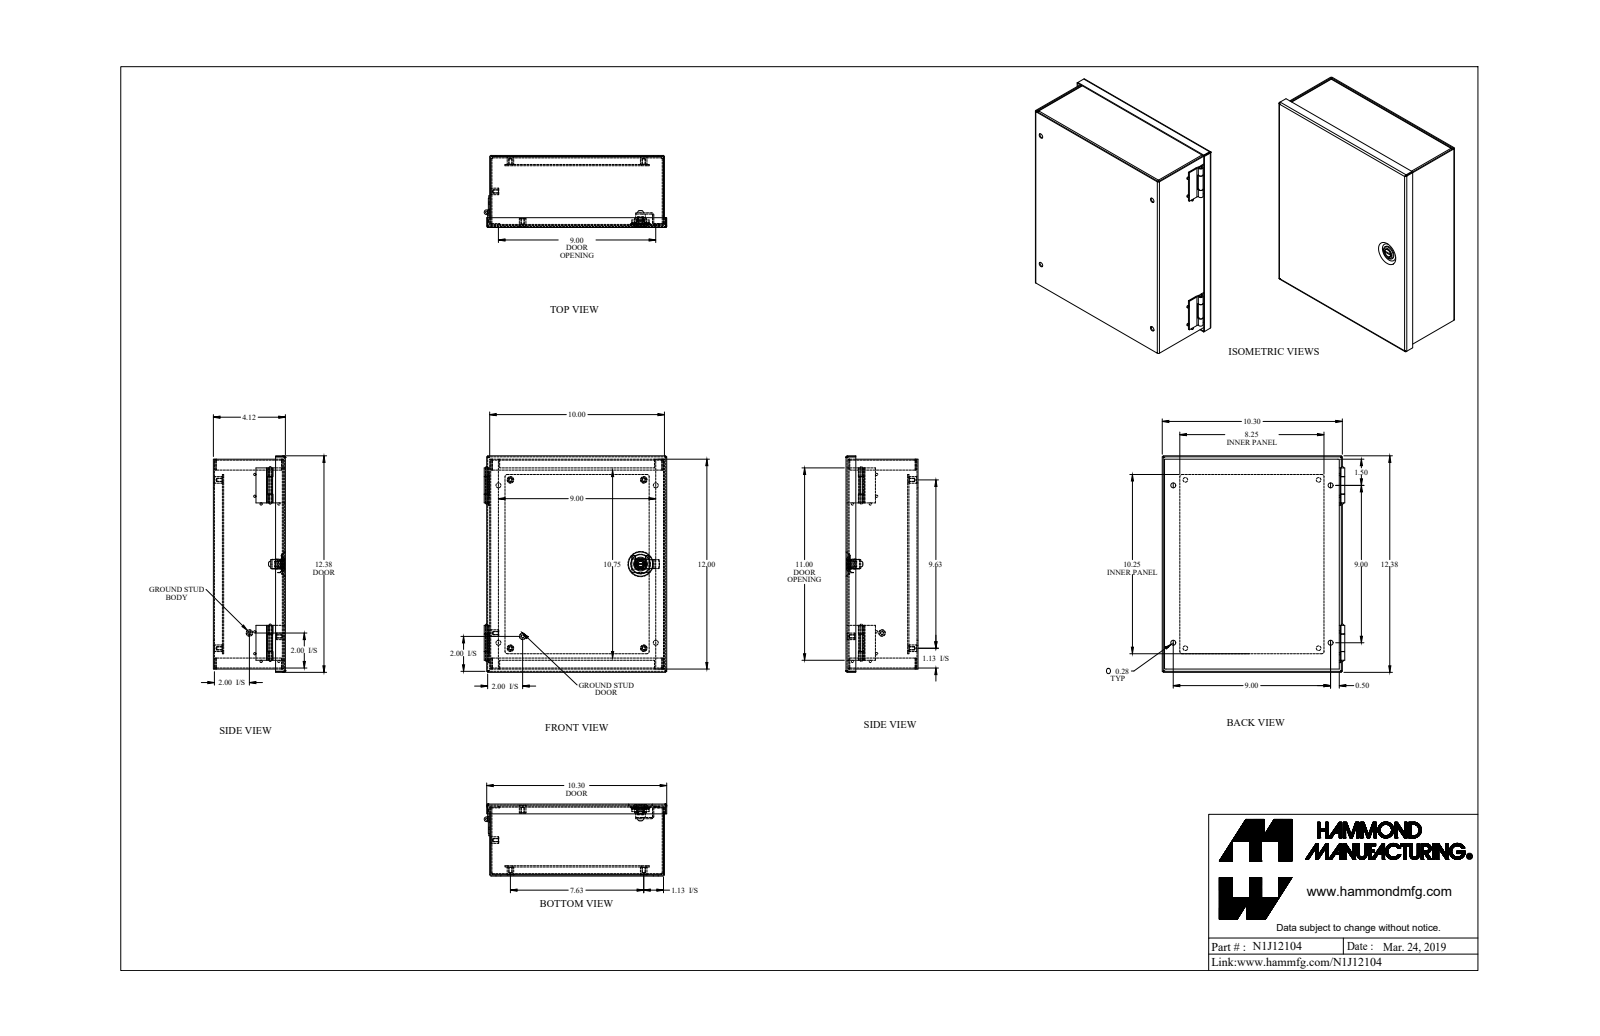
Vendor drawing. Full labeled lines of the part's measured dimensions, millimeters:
Part name (STEP PRODUCT): N1J12104
STEP written by: SolidWorks 2018 (AUTOMOTIVE_DESIGN)
Units: millimetres
Bodies: 18 solids, 477 faces (224 planar, 188 cylindrical, 65 other)
Overall size (bounding box): 314.5 × 265.3 × 104.6
Volume: 564 000 mm³ · Surface area: 752 300 mm²
Round holes (diameter × count): ⌀4 ×6, ⌀6.7 ×4, ⌀7.1 ×4, ⌀3.2 ×1, ⌀8.1 ×1, ⌀12.1 ×1
Round bosses / shafts (diameter × count): ⌀3.3 ×8, ⌀9.5 ×6, ⌀20 ×1, ⌀13.9 ×1, ⌀12 ×1, ⌀11.9 ×1, ⌀9.3 ×1, ⌀8.1 ×1
Partial cylindrical surfaces — rounded edges, fillets, slot ends (radius × count): R0.7 ×16, R2.2 ×16, R0.3 ×4, R2.5 ×4, R3.2 ×4, R0.9 ×2, R2 ×2, R6.4 ×2
Main face-to-face distances: 1.4, 103.1, 101.7, 104.6, 252.6, 1.8, 13.1, 11.7, 90, 91.5
Hole centre spacings: 19.2, 211.3, 228.6, 237.2, 317.1, 116.4, 122.3, 193.7
